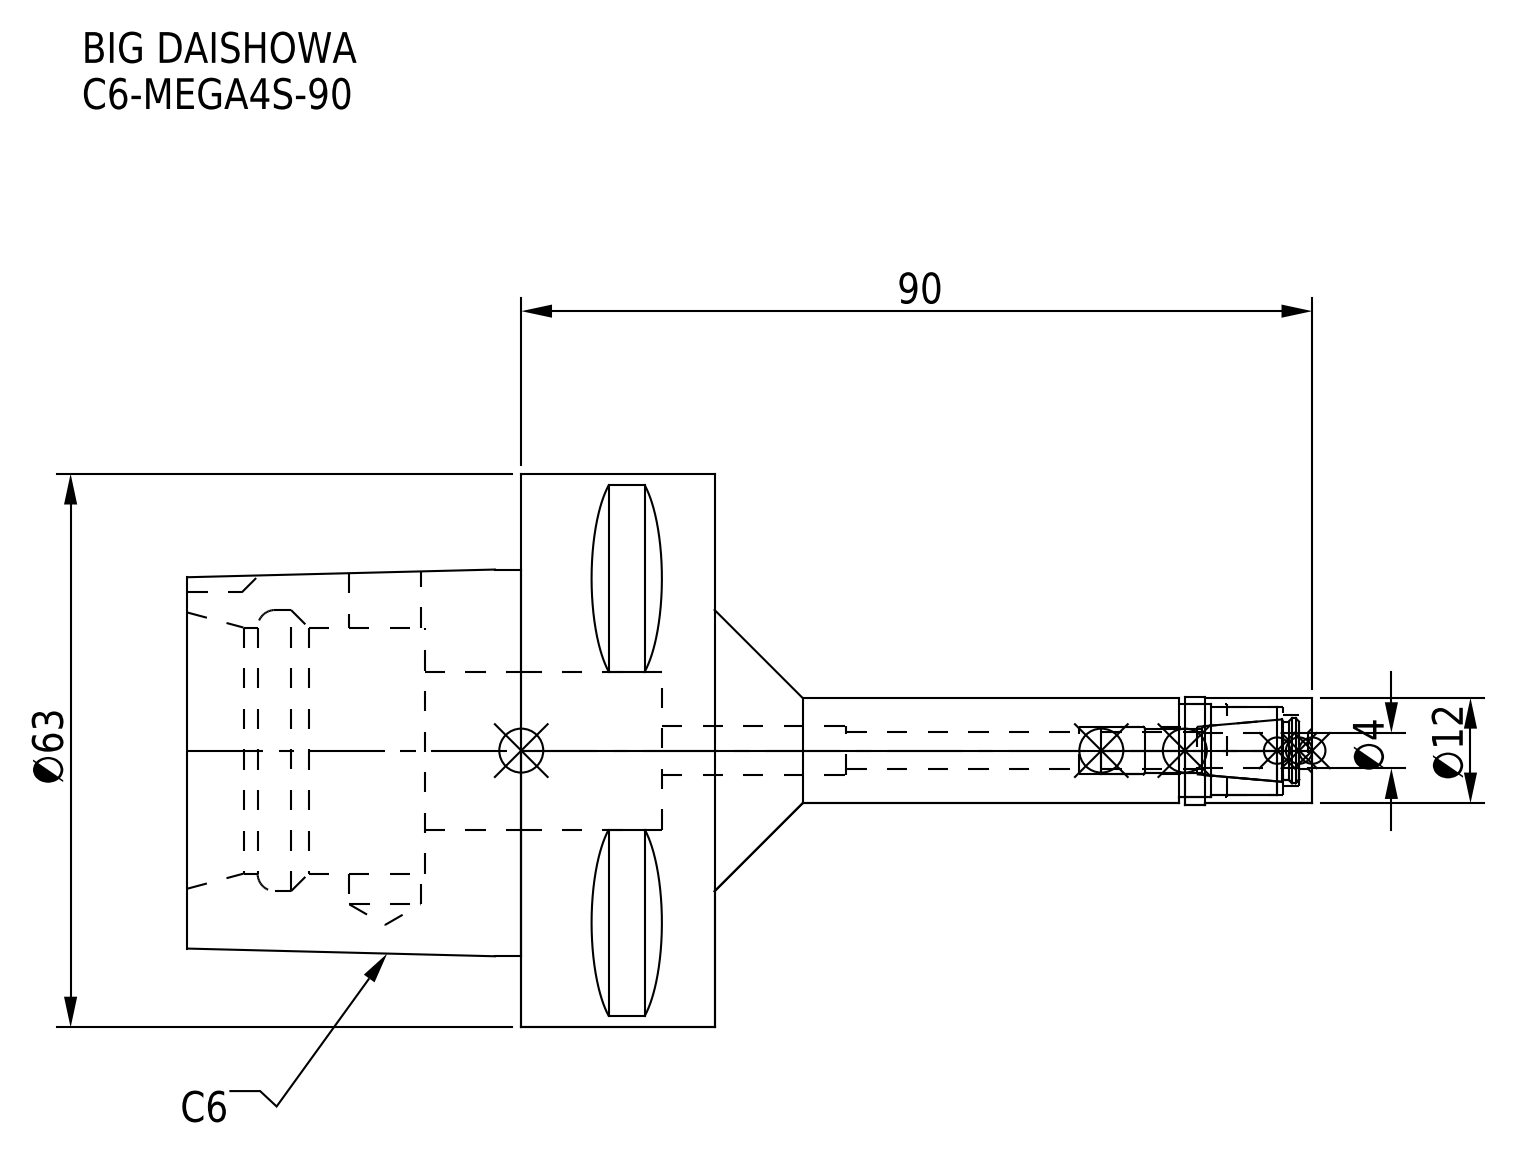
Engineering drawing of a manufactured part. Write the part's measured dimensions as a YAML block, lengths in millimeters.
part_name: "MGN4S_1.stp; C6-MEGA4S-90_1.stp; C6-MEGA4S-90-040-FreeParts; C6-MEGA4S-90-040_ASM.stp (+3 more)"
step_written_by: "SolidWorks 2019 (CONFIG_CONTROL_DESIGN)"
units: millimeters
bodies: {solids: 2, faces: 93, planar: 38, cylindrical: 39, other: 16}
overall_size: [128, 63, 63]
volume: 105571
surface_area: 24654
round_holes:
  - {diameter: 4.1, count: 1}
  - {diameter: 4.2, count: 1}
  - {diameter: 5.4, count: 1}
  - {diameter: 5.5, count: 1}
  - {diameter: 8, count: 1}
  - {diameter: 8.1, count: 1}
  - {diameter: 10, count: 1}
  - {diameter: 10.5, count: 1}
  - {diameter: 18, count: 1}
  - {diameter: 28, count: 1}
  - {diameter: 32, count: 1}
round_bosses_or_shafts:
  - {diameter: 63, count: 1}
  - {diameter: 12.3, count: 1}
  - {diameter: 12, count: 1}
partial_cylinders:
  - {radius: 5, count: 1}
face_to_face_distances: [22, 27, 60, 38, 33, 11, 24.89, 55.4, 6, 16]
